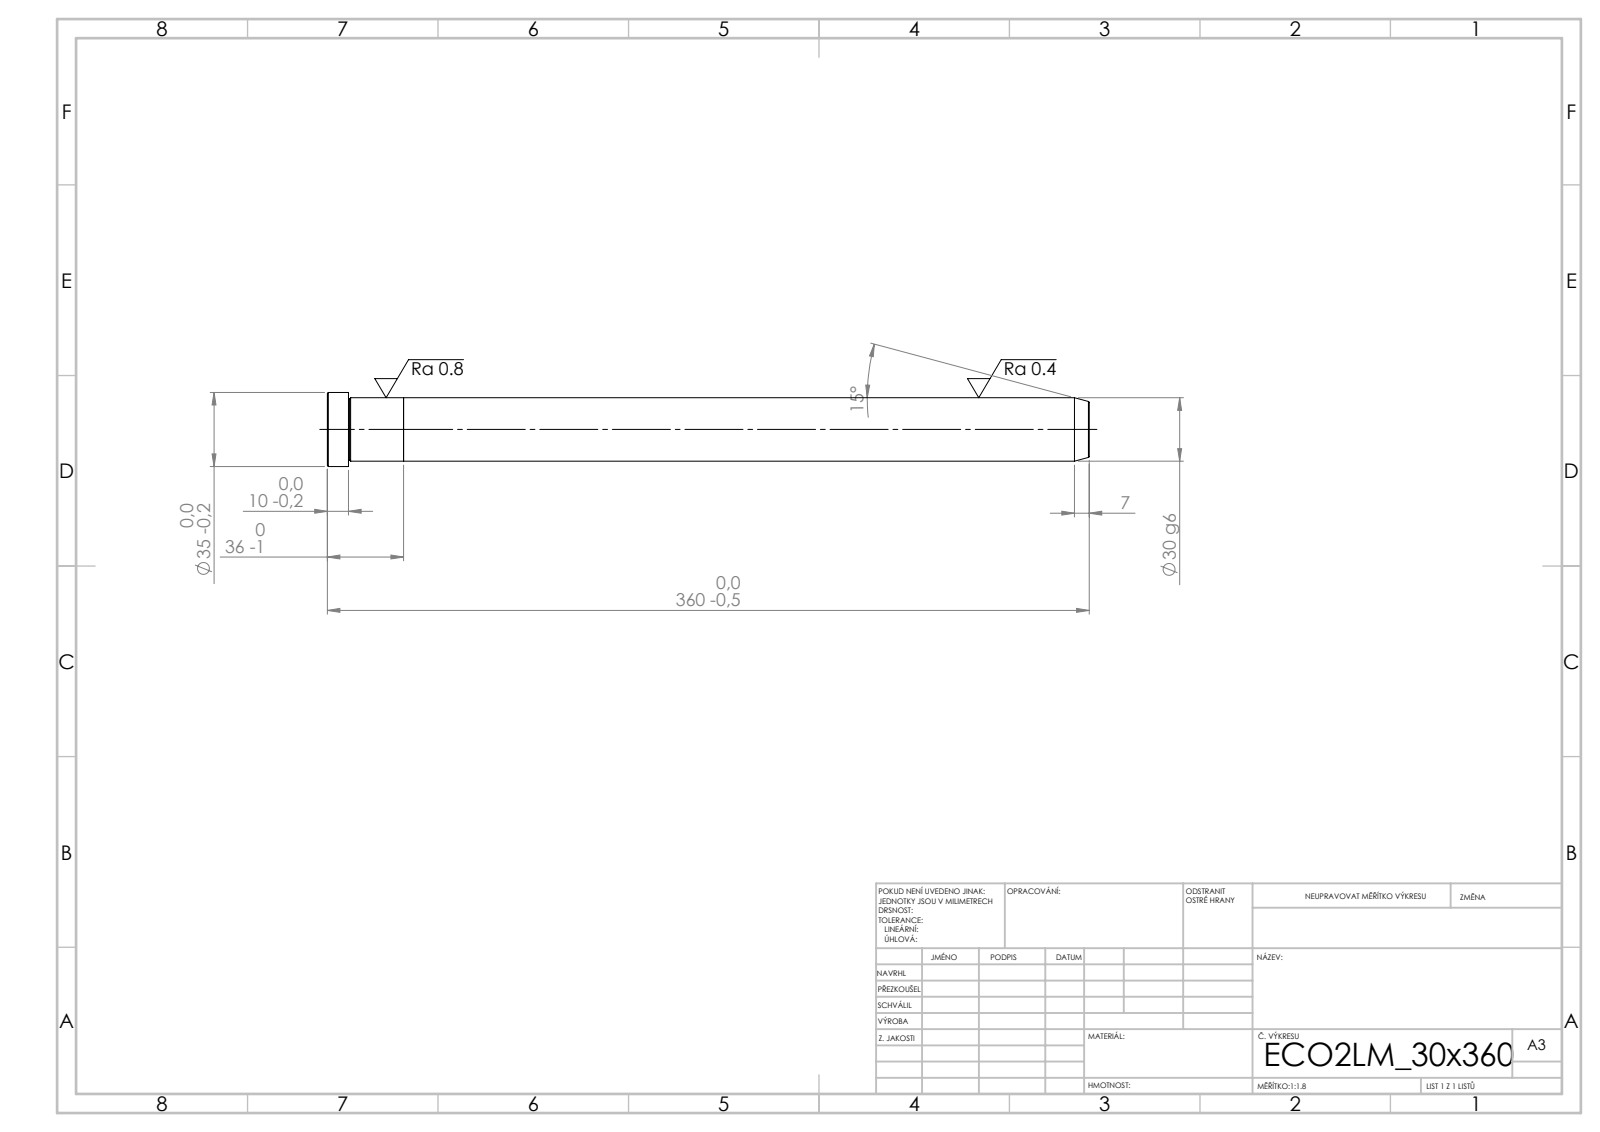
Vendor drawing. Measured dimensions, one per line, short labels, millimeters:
written by: SolidWorks 2019 (CONFIG_CONTROL_DESIGN)
unit: mm
bodies: 2 solids, 21 faces (5 planar, 6 cylindrical, 10 other)
size: 360 × 35 × 35
volume: 256 376 mm³; area: 37 248 mm²
bosses: 1× ⌀35, 1× ⌀30
face distances: 36, 324, 360, 350, 26, 10
